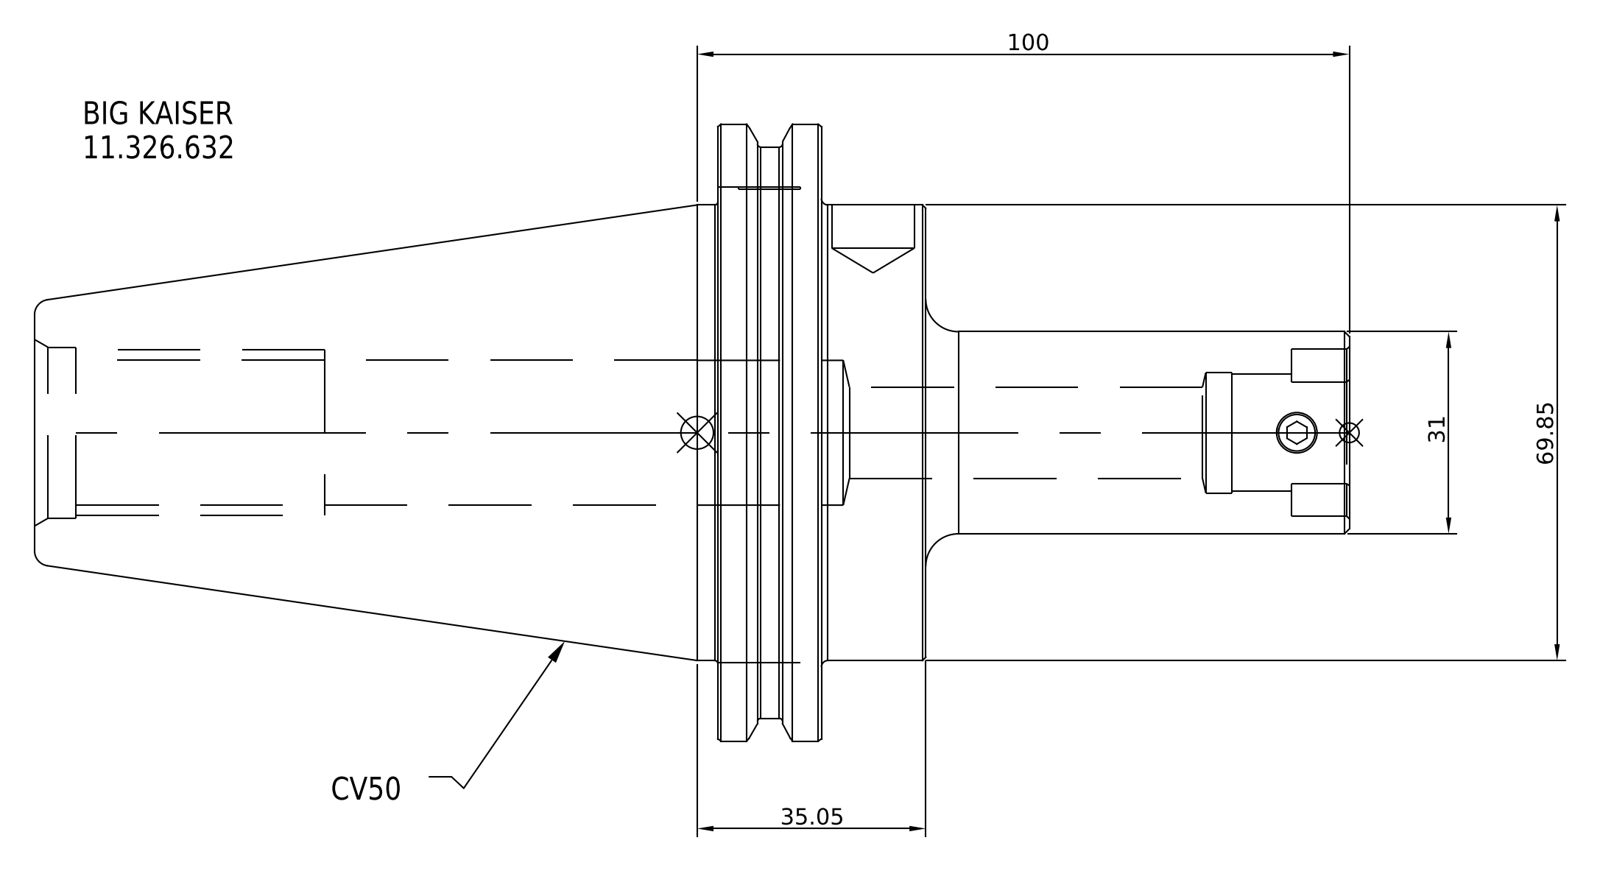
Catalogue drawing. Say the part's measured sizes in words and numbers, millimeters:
The part is named "11.326.632". Its 3-D file was written by "SolidWorks 2021 (CONFIG_CONTROL_DESIGN)". It is 1 solid with 16 faces: 7 planar, 6 cylindrical and 3 other. Overall it measures 201.6 by 98.43 by 98.43 millimeters. Its volume is 491 541 cubic millimeters and its surface area 47 303 square millimeters. Round bosses or shafts: 1 of diameter 98.43, 1 of diameter 91.29, 1 of diameter 69.85, 1 of diameter 31. The main face-to-face distances are 17.55, 15.95, 33.5, 136.6, 120.65, 103.1, 65, 80.95, 98.5, 201.6.
